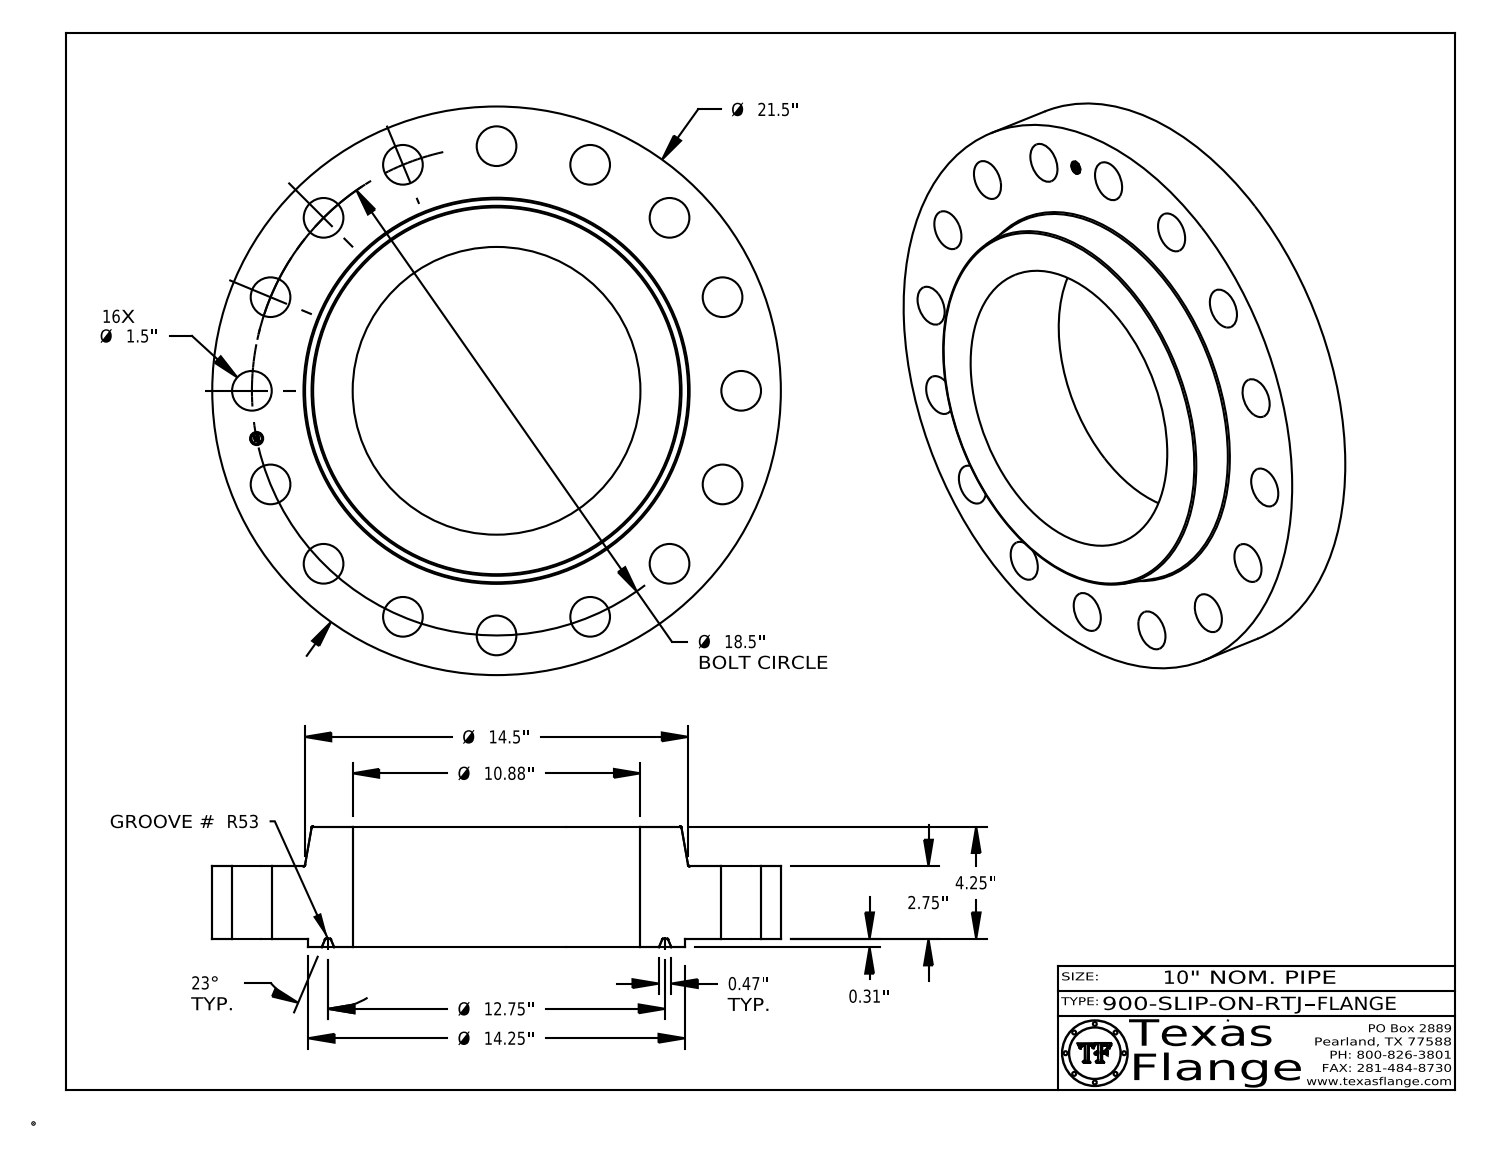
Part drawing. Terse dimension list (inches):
name: 900-SLIP-ON-RTJ
written by: CATIA V5 STEP AP214 (AUTOMOTIVE_DESIGN)
unit: in
bodies: 1 solid, 443 faces (371 planar, 58 cylindrical, 14 other)
size: 21.5 × 21.5 × 4.563
volume: 780.9 in³; area: 1 118 in²
holes: 16× ⌀1.5, 1× ⌀0.495, 1× ⌀10.88
bosses: 8× ⌀0.03, 1× ⌀21.5, 1× ⌀14.25, 1× ⌀0.39
face distances: 2.75, 4.25, 1.5, 0.313, 3.063, 4.563, 3.048, 2.735, 0.015, 1.515
hole spacings: 15.382, 7.08, 9.25, 13.081, 3.609, 3.609, 10.278, 10.278
